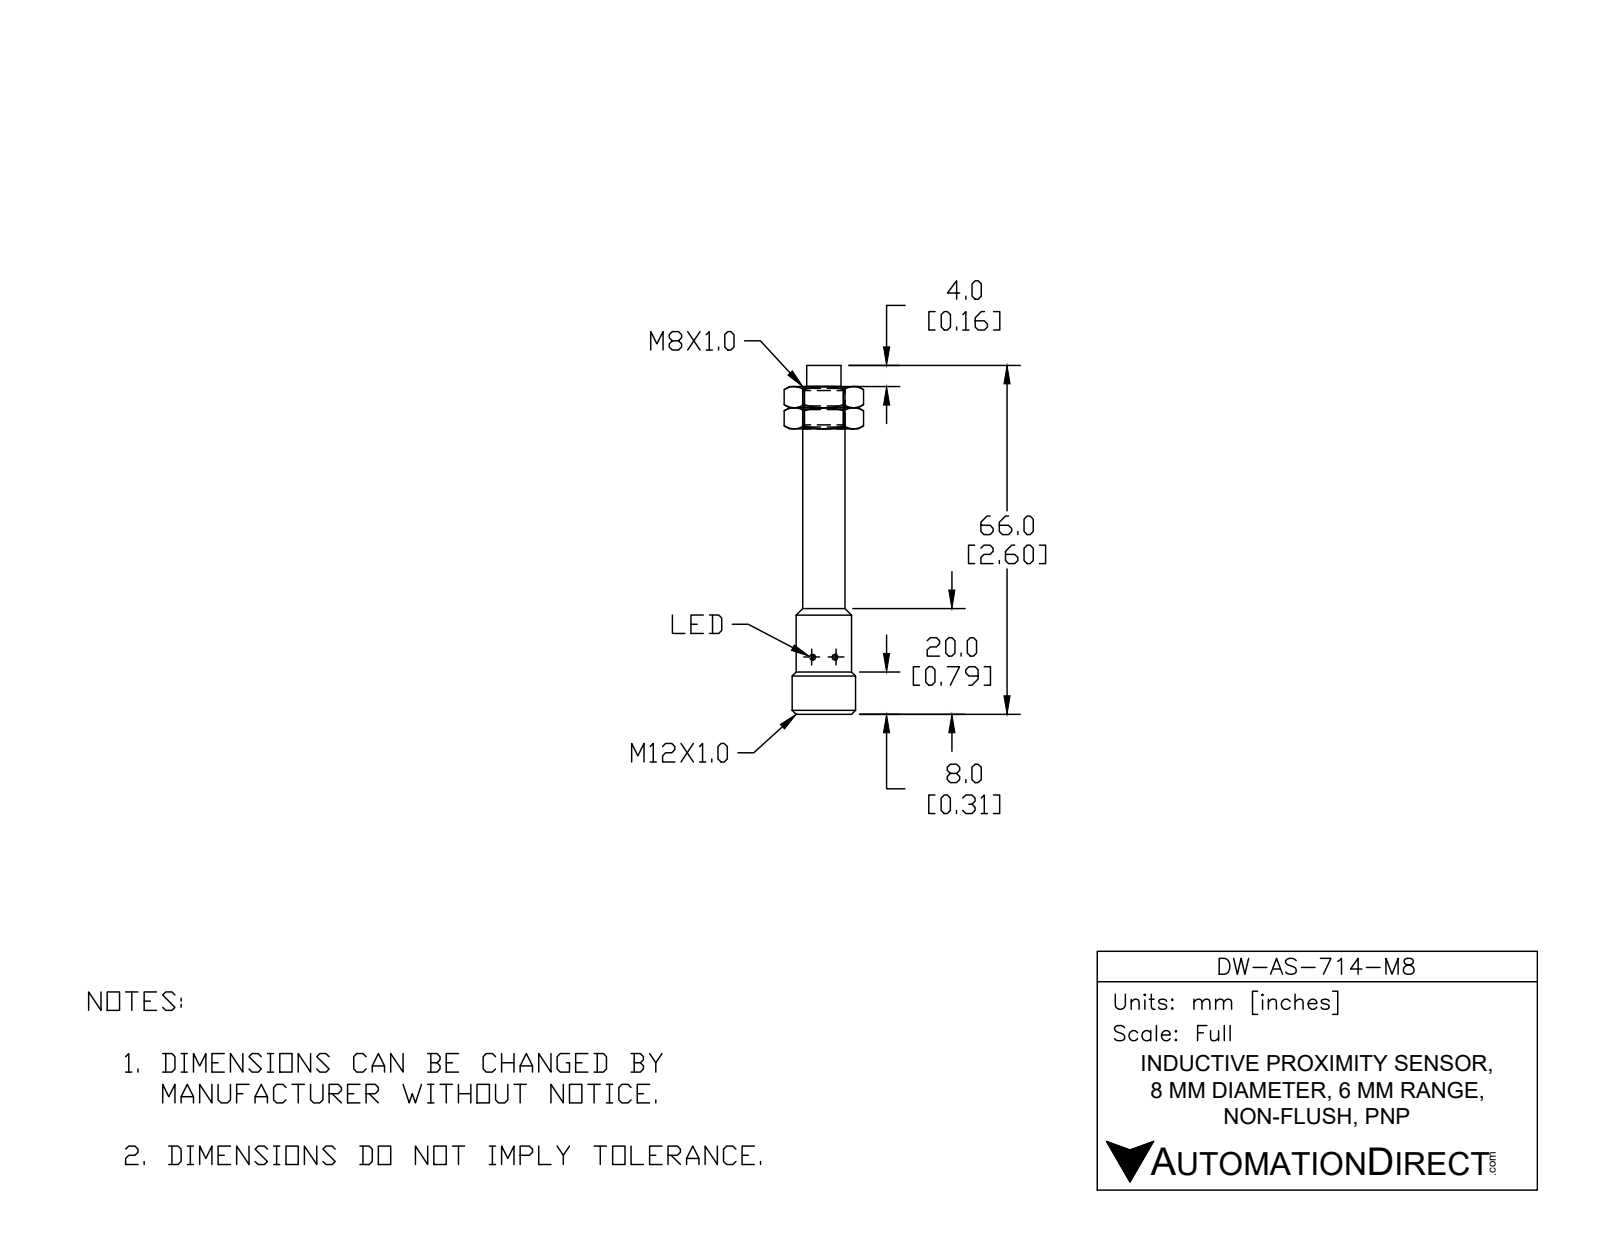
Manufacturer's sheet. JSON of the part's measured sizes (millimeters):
{"part_name": "DW-AS-714-M8", "step_written_by": "SolidWorks 2017 (AUTOMOTIVE_DESIGN)", "units": "millimeters", "bodies": {"solids": 1, "faces": 43, "planar": 7, "cylindrical": 26, "other": 10}, "overall_size": [66, 12, 12], "volume_mm3": 3570, "surface_area_mm2": 2513, "round_holes": [[3, 2], [8.5, 1]], "round_bosses_or_shafts": [[1, 4], [12, 1], [10.5, 1], [8, 1], [6.5, 1]], "partial_cylinders_radius": [[0.5, 2], [0.6, 1], [4.6, 1], [4.9, 1]], "face_to_face_distances": [8.7, 57.3, 66, 46, 11.3, 20, 1.1, 64.5, 18.5, 7.2]}
